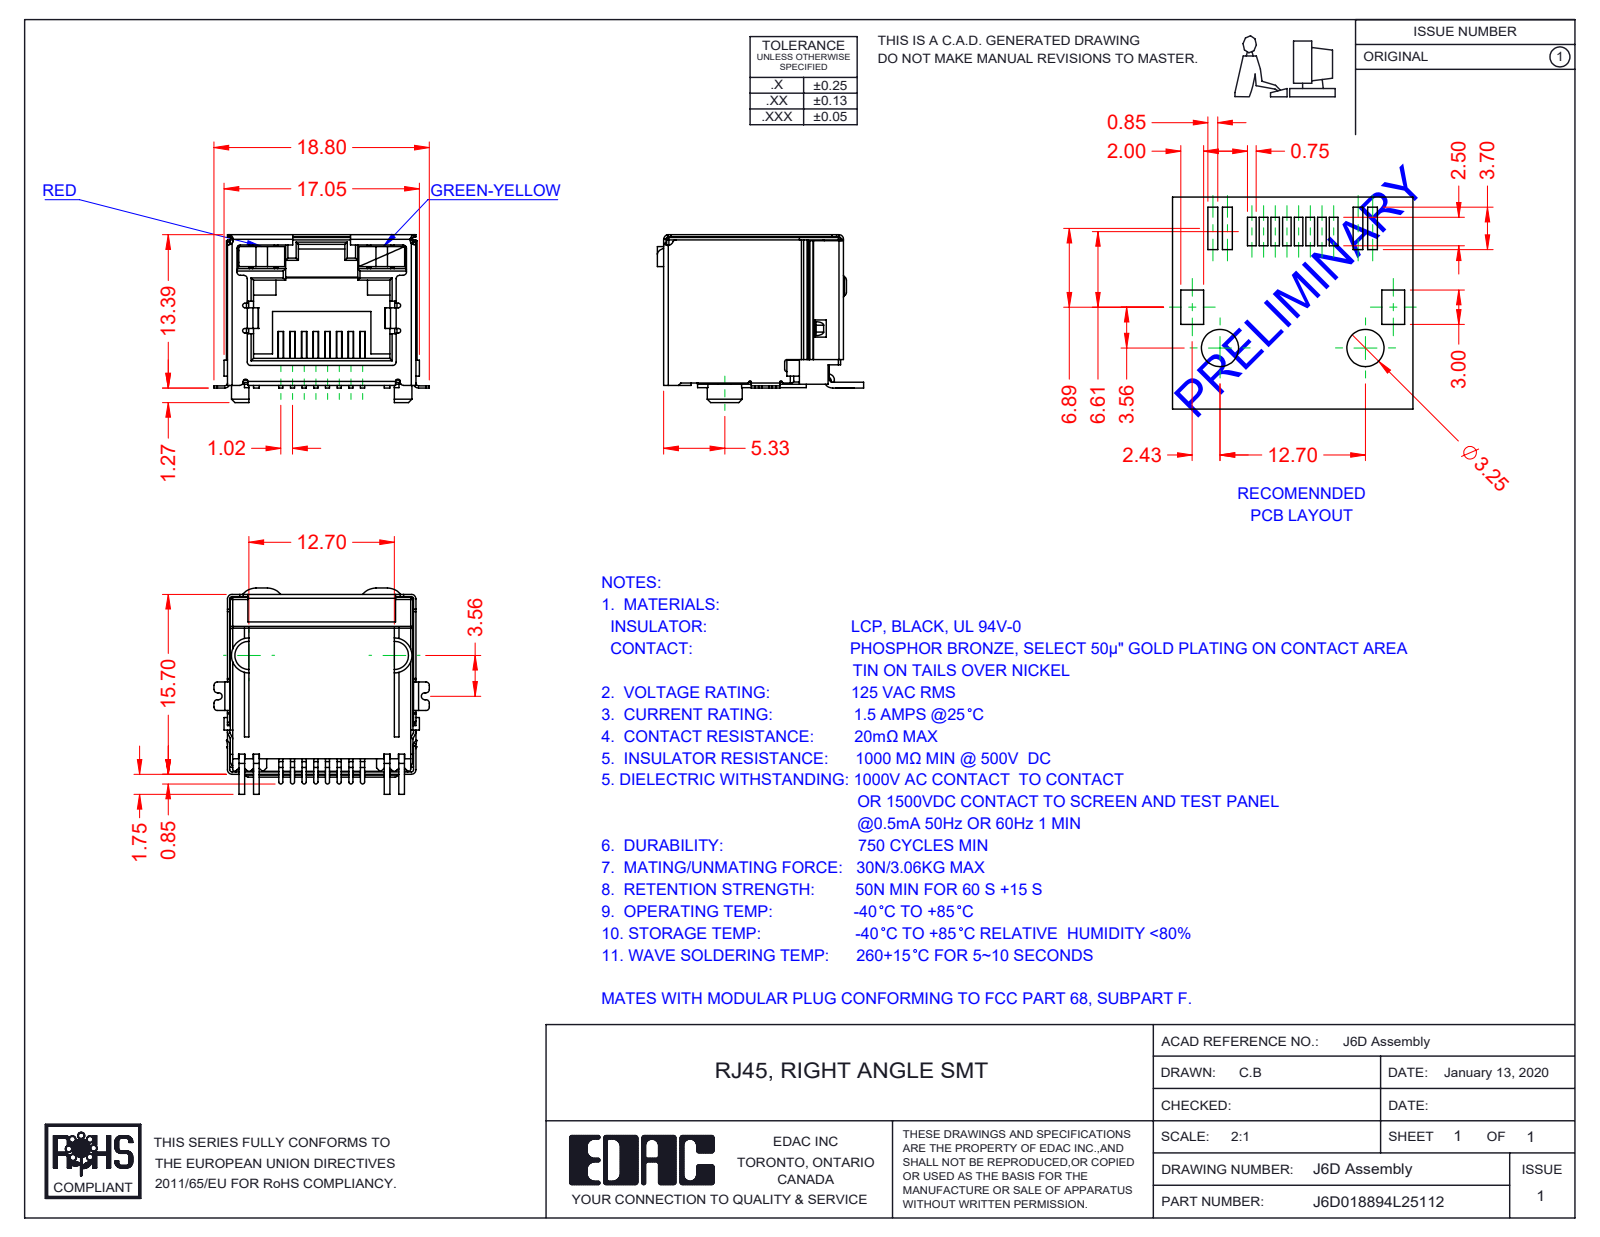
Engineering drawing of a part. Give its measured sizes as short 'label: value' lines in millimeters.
name: 6D LED RH_5-Green-Yellow; 6D Contacts; 6D LED LH_2-Red; 6D Insulator (+2 more)
written by: SolidWorks 2016 (CONFIG_CONTROL_DESIGN)
unit: mm
bodies: 12 solids, 896 faces (645 planar, 218 cylindrical, 33 other)
size: 18.8 × 18 × 14.65
volume: 1 804 mm³; area: 4 898 mm²
rounds: 39× R0.3, 37× R0.2, 16× R0.4, 12× R0.1, 8× R0.15, 8× R0.18, 6× R0.5, 5× R1.5
face distances: 16, 16.25, 16.2, 2.25, 1, 15.95, 16.05, 12.8, 0.45, 16.45
